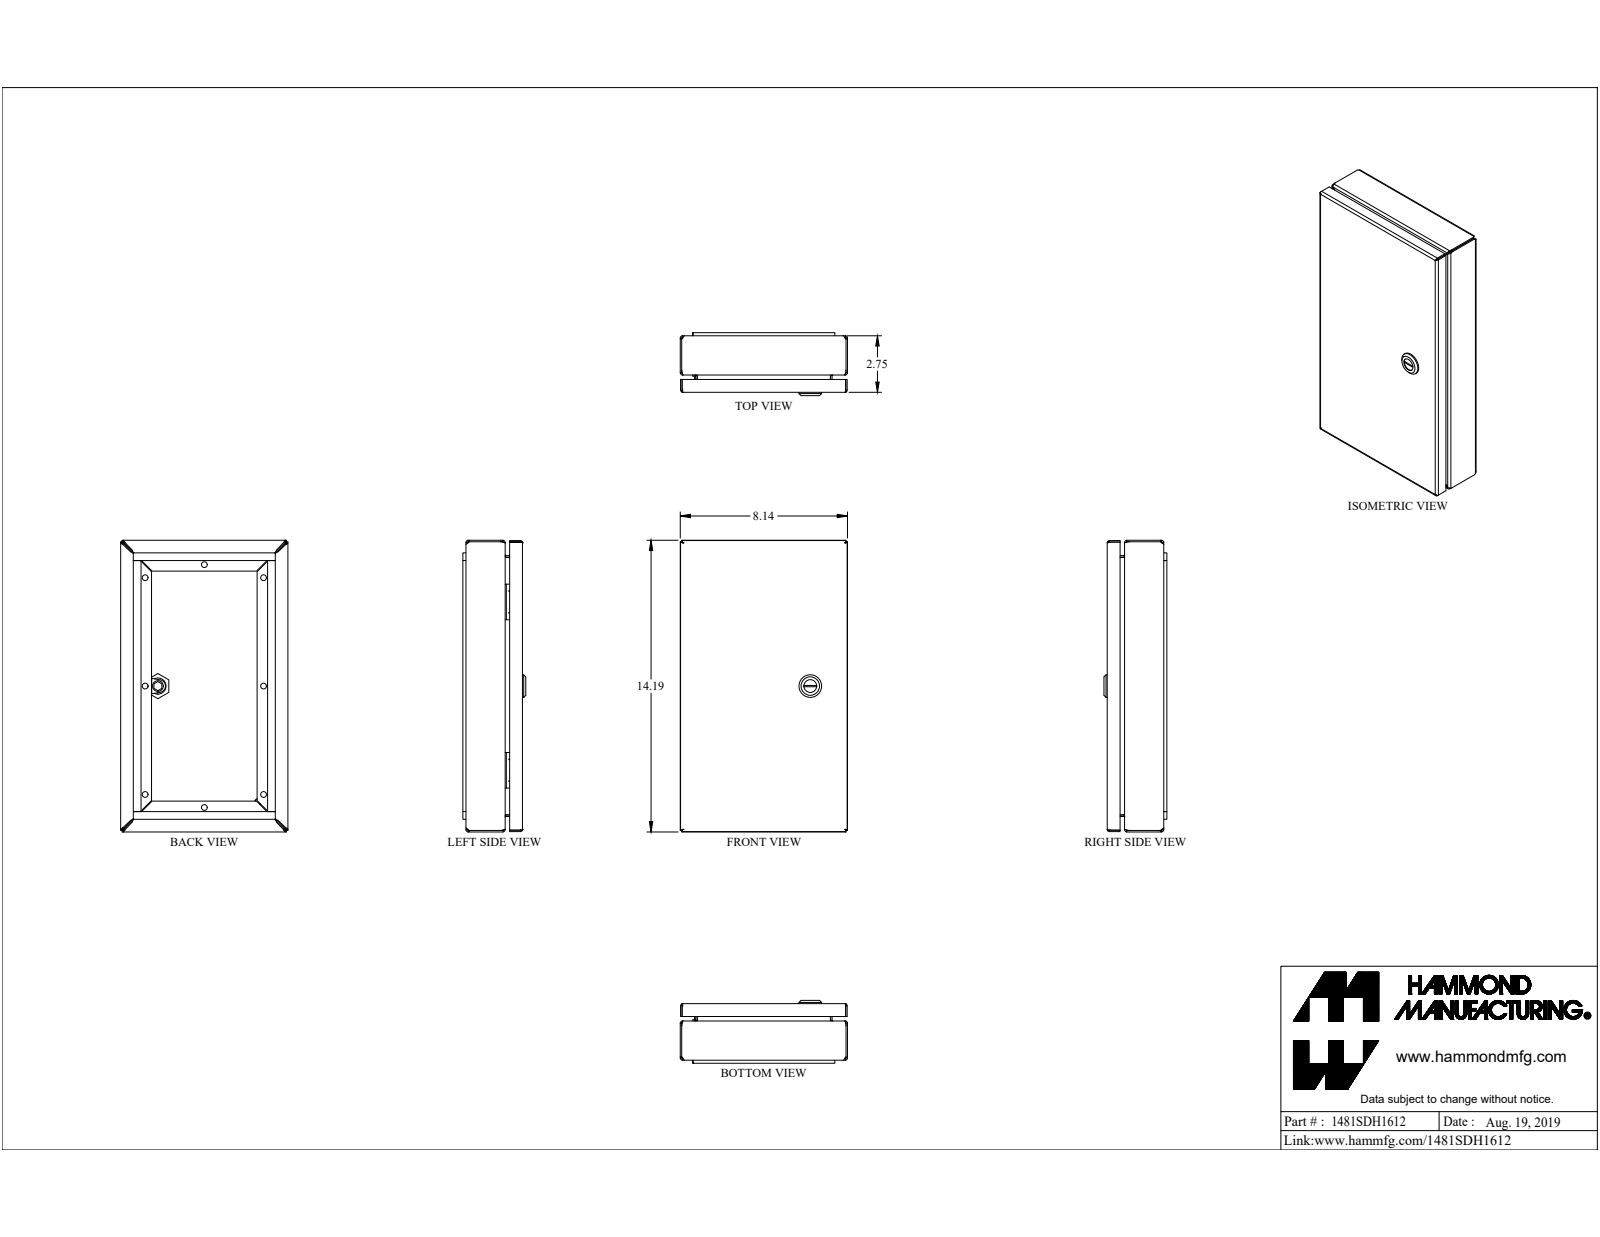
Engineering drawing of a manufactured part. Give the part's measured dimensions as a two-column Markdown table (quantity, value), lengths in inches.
| quantity | value |
| --- | --- |
| part name | 1481SDH1612 |
| STEP written by | SolidWorks 2019 (CONFIG_CONTROL_DESIGN) |
| units | inches |
| bodies | 23 solids, 614 faces (348 planar, 168 cylindrical, 98 other) |
| overall size | 14.19 × 8.14 × 3.061 |
| volume | 32.41 in³ |
| surface area | 837.4 in² |
| round holes (diameter × count) | 0.281 × 8, 0.172 × 1, 0.232 × 1, 0.24 × 1, 0.242 × 1, 0.625 × 1, 0.785 × 1 |
| round bosses / shafts (diameter × count) | 1.1 × 1, 0.525 × 1, 0.455 × 1, 0.398 × 1, 0.356 × 1, 0.313 × 1, 0.292 × 1, 0.25 × 1 |
| partial cylindrical surfaces (radius × count) | 0.036 × 28, 0.108 × 28, 0.382 × 12, 19.003 × 8, 0.006 × 4, 0.062 × 4, 0.25 × 4, 0.499 × 4 |
| main face-to-face distances | 0.072, 0.072, 1.736, 2.579, 8.068, 2.651, 2.579, 0.843, 2.679, 1.836 |
| hole center spacings | 2.951, 11.545, 5.764, 5.273, 5.273, 6.572, 6.572, 7.812 |
